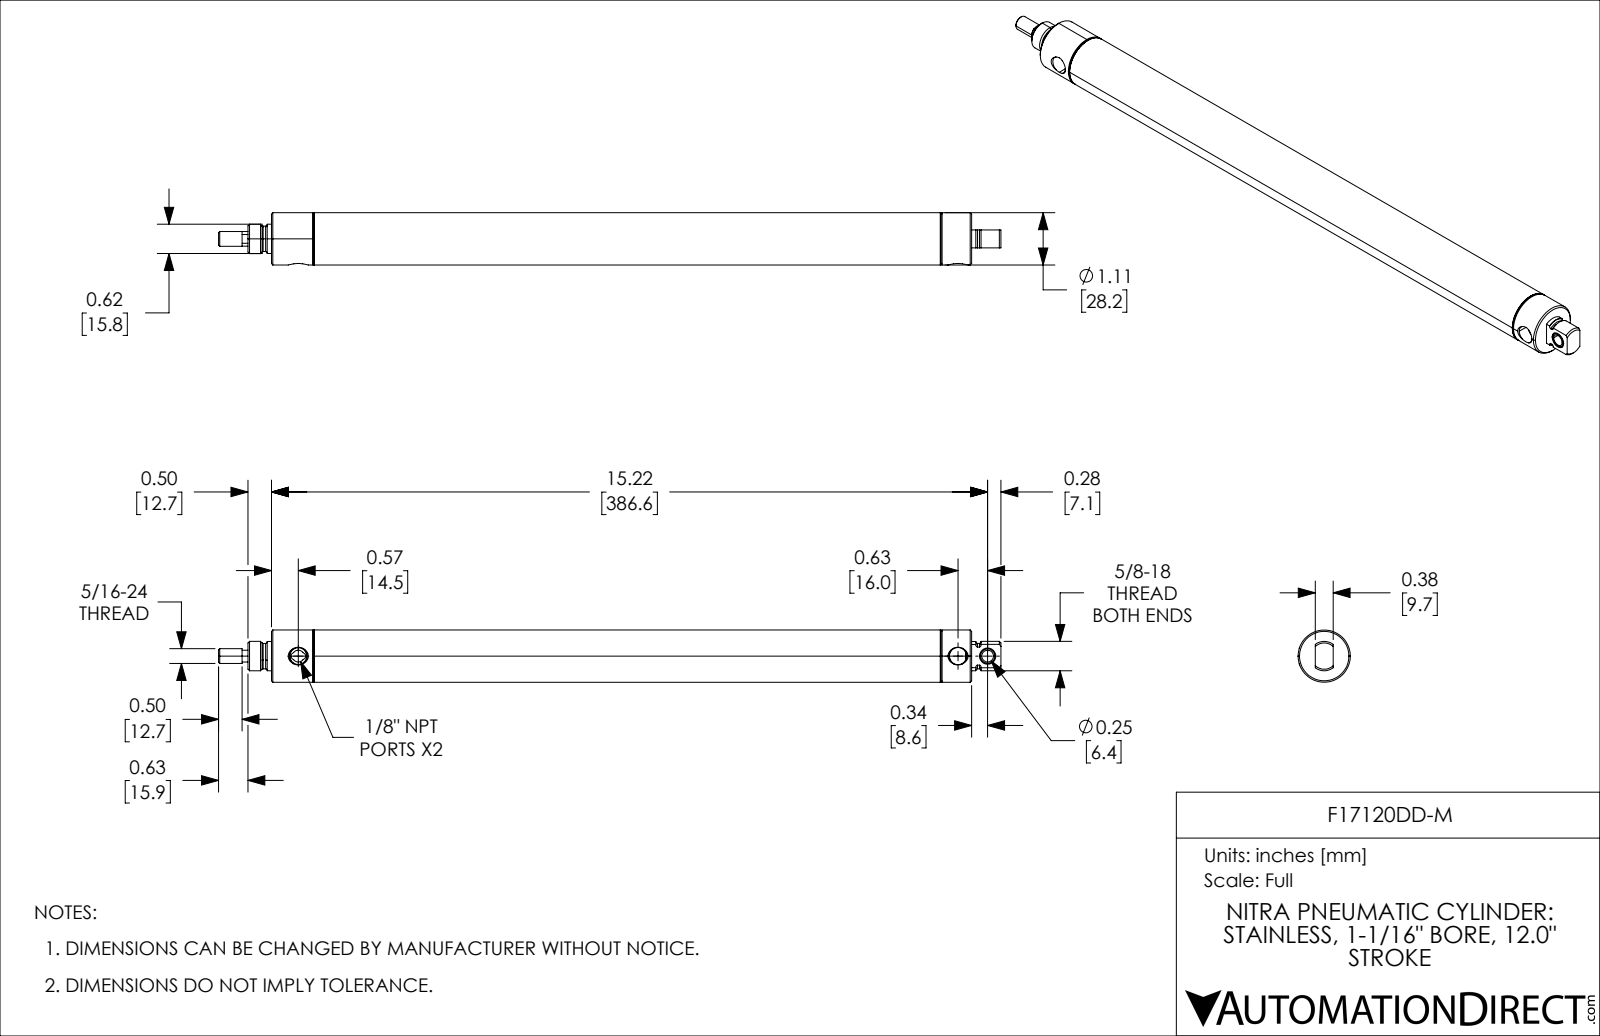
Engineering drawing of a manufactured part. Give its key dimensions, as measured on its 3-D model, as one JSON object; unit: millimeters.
{"part_name": "F17120DD-M_7; F17120DD-M_3; F17120DD-M_11; F17120DD-M (+2 more)", "step_written_by": "SolidWorks 2021 (CONFIG_CONTROL_DESIGN)", "units": "millimeters", "bodies": {"solids": 5, "faces": 156, "planar": 30, "cylindrical": 58, "other": 68}, "overall_size": [422.27, 28.19, 28.19], "volume_mm3": 73693, "surface_area_mm2": 82799, "round_holes": [[6.38, 1], [8.53, 1], [8.78, 1], [9.25, 1], [9.53, 1], [19.05, 1], [25.7, 1]], "round_bosses_or_shafts": [[28.19, 1], [27.23, 1], [15.88, 1], [15.81, 1], [13.68, 1], [7.94, 1], [7.92, 1]], "partial_cylinders_radius": [[3.17, 1], [6.84, 1]], "face_to_face_distances": [22.22, 304.8, 327.02, 349.35, 44.55, 22.33, 28.58, 333.38, 355.6, 377.93], "hole_center_spacings": [16.01]}
